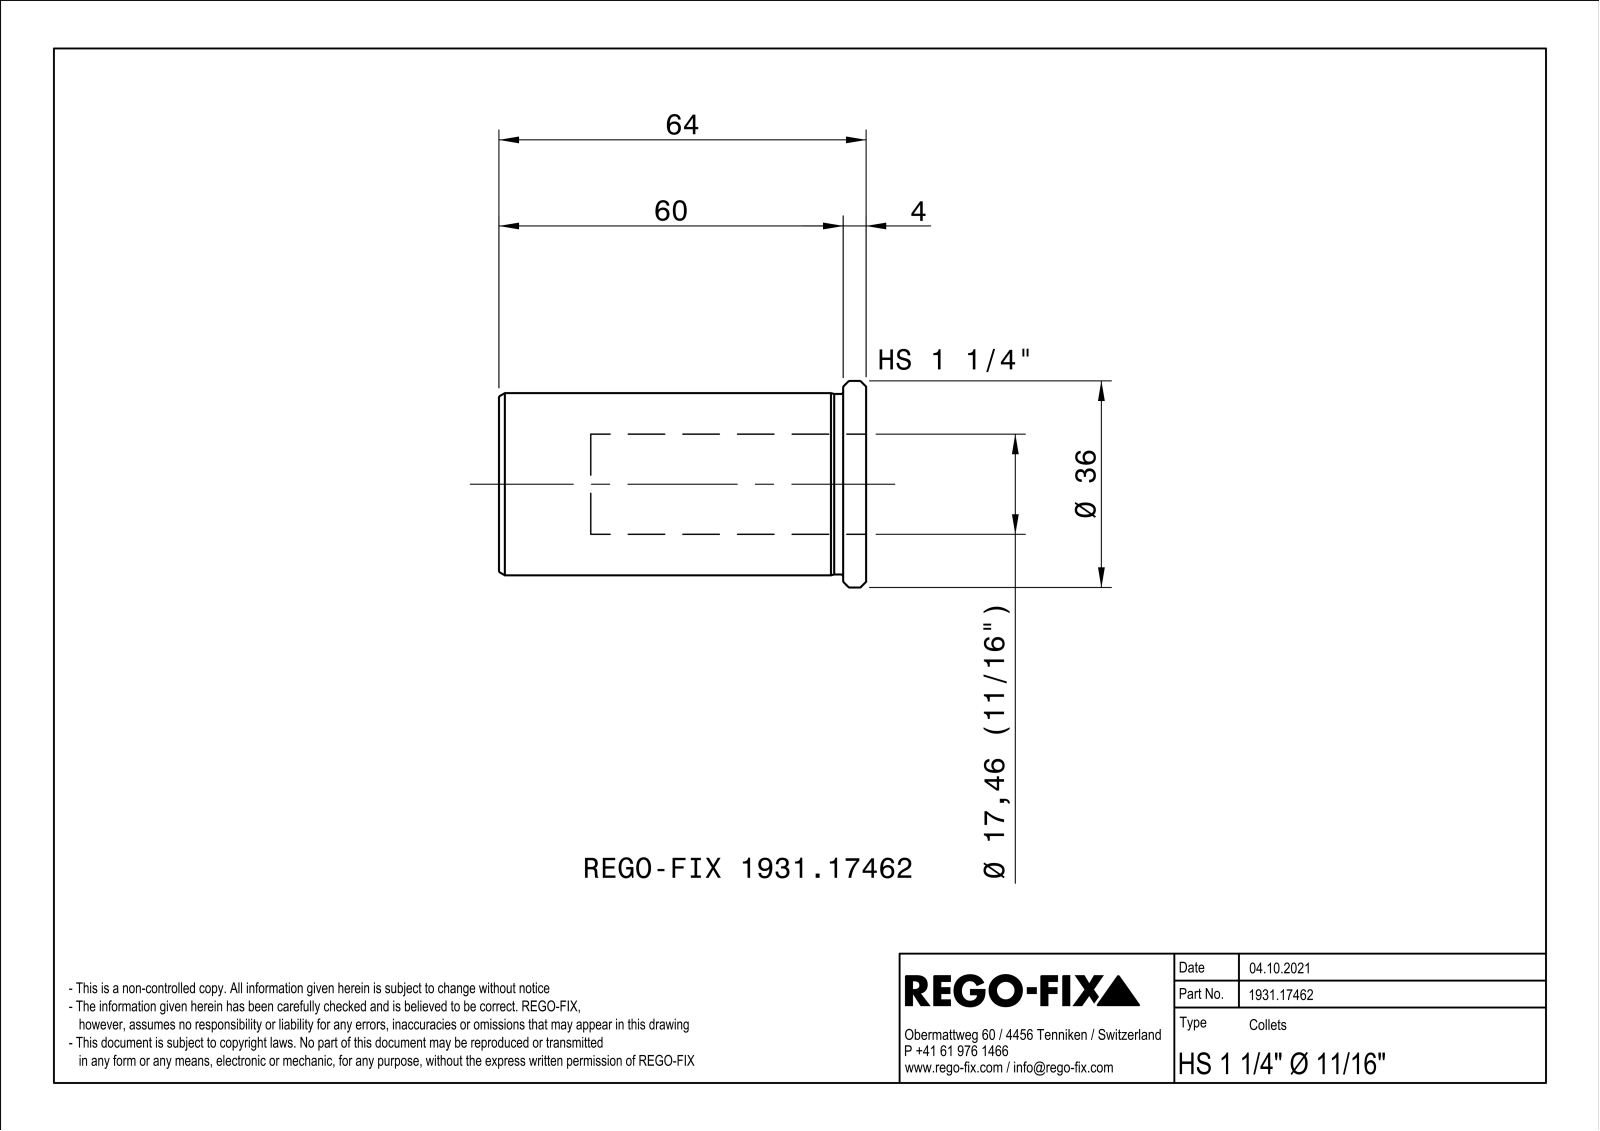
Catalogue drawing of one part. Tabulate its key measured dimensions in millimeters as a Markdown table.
| quantity | value |
| --- | --- |
| part name | NOCUT |
| STEP written by | SIEMENS PLM Software Solid Edge ST10 (AUTOMOTIVE_DESIGN) |
| units | millimeters |
| bodies | 1 solid, 70 faces (22 planar, 11 cylindrical, 37 other) |
| overall size | 64 × 35.99 × 35.99 |
| volume | 30 772 mm³ |
| surface area | 13 615 mm² |
| round holes (diameter × count) | 17.46 × 1, 26.5 × 1 |
| round bosses / shafts (diameter × count) | 36 × 1, 31.75 × 1, 31.45 × 1 |
| main face-to-face distances | 1, 64, 4, 60 |
